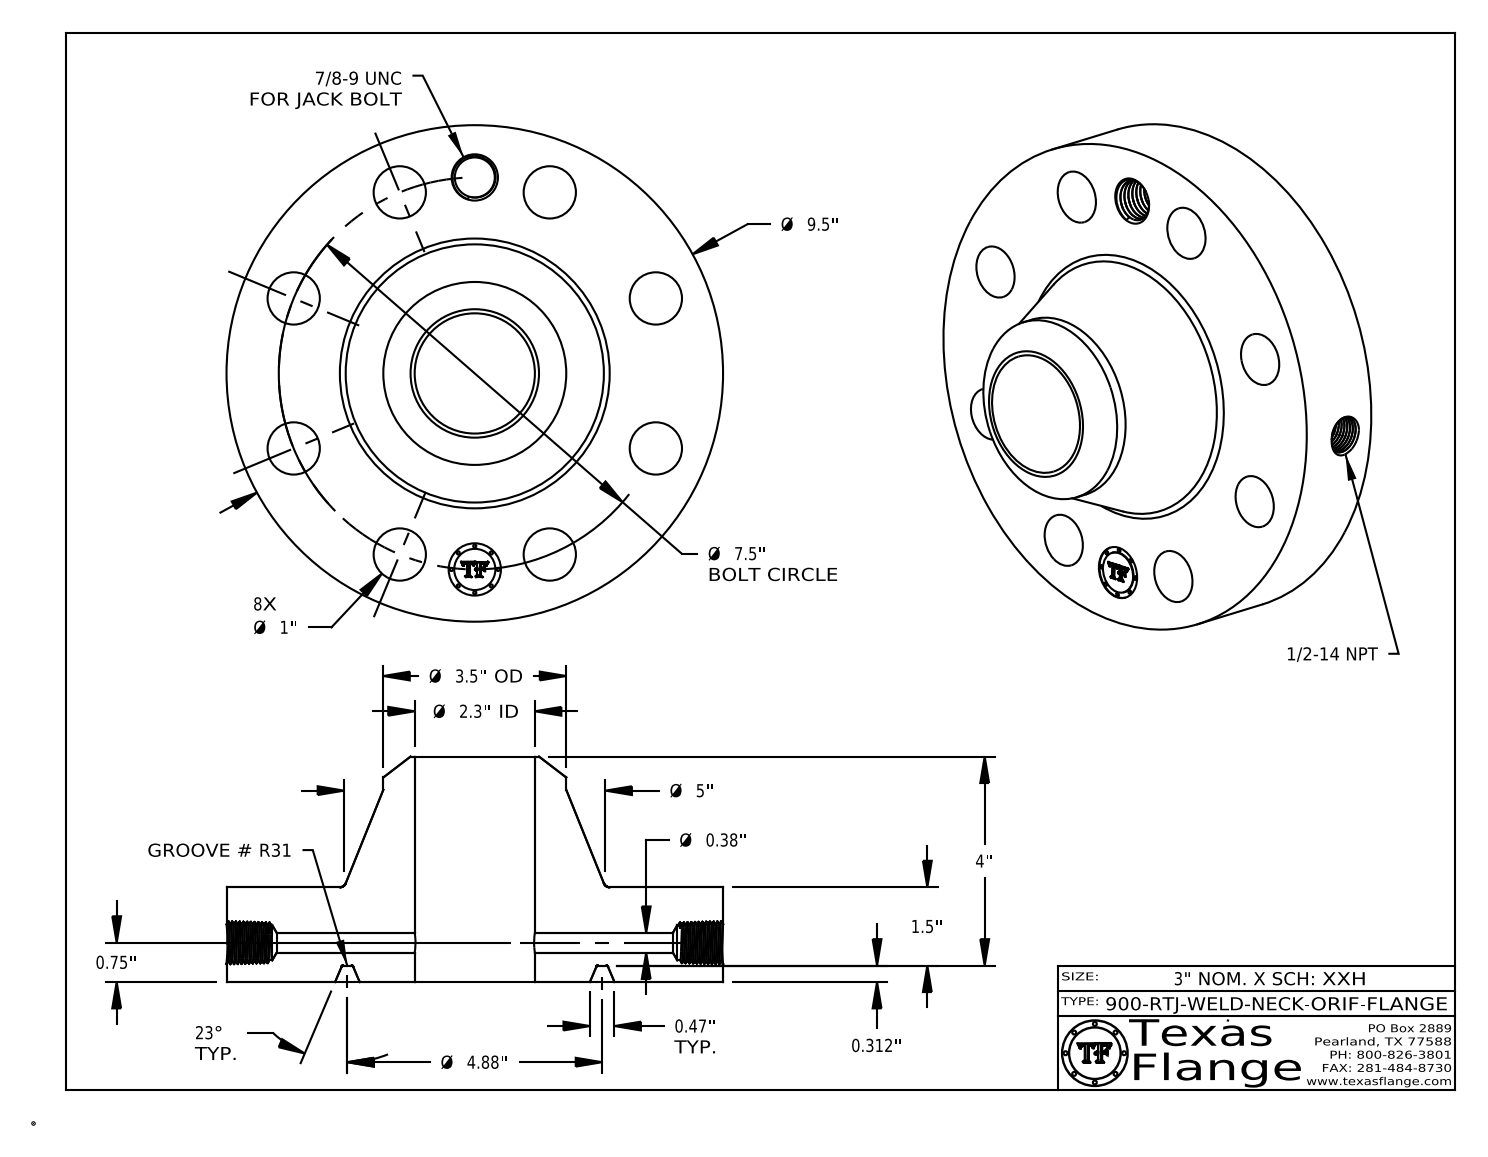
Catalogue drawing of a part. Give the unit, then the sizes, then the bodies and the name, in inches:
Units: inches
Overall size (bounding box): 9.5 × 9.5 × 4.312
Round holes (diameter × count): ⌀1 ×9, ⌀0.375 ×1, ⌀0.672 ×1, ⌀0.766 ×1, ⌀2.3 ×1
Round bosses / shafts (diameter × count): ⌀0.061 ×8, ⌀9.5 ×1, ⌀3.5 ×1, ⌀0.788 ×1
Main face-to-face distances: 1.812, 0.312, 1.5, 4.312, 4, 2.5, 1.797, 1.485, 0.015, 2.515
Hole centre spacings: 3.75, 2.87, 5.303, 6.929, 7.5, 1.463, 4.167, 6.236
Volume: 127 in³ · Surface area: 296.7 in²
Bodies: 1 solid, 784 faces (370 planar, 94 cylindrical, 320 other)
Part name (STEP PRODUCT): 900-RTJ-WELD-NECK
STEP written by: CATIA V5 STEP AP214 (AUTOMOTIVE_DESIGN)
